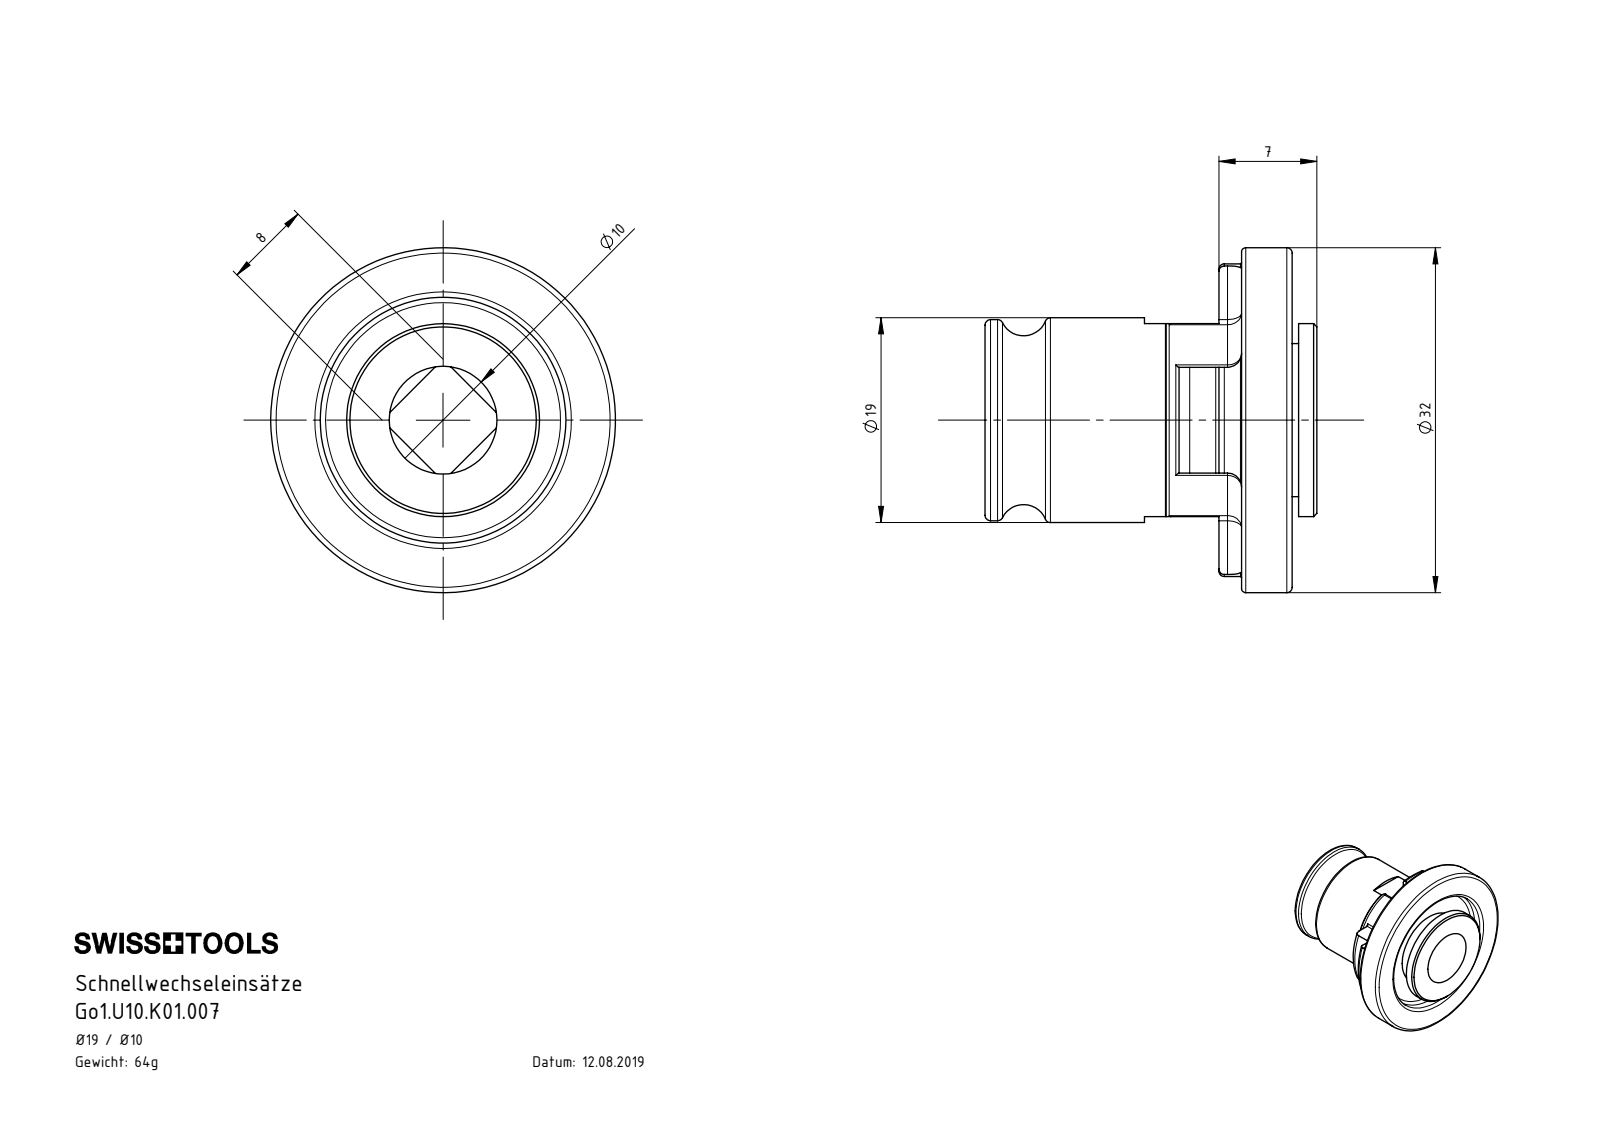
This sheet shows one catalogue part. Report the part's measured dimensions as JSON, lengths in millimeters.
{"part_name": "Go1.U10.K01.007", "step_written_by": "SolidWorks 2017 (AUTOMOTIVE_DESIGN)", "units": "millimeters", "bodies": {"solids": 1, "faces": 113, "planar": 36, "cylindrical": 32, "other": 45}, "overall_size": [32, 32, 30.8], "volume_mm3": 8171, "surface_area_mm2": 4952, "round_holes": [[10, 1], [11.4, 1], [22.8, 1]], "round_bosses_or_shafts": [[32, 1], [19, 1], [18.65, 1], [18.52, 1], [17.9, 1], [14.2, 1]], "partial_cylinders_radius": [[0.5, 8], [1.3, 4], [12.4, 1], [14.5, 1]], "face_to_face_distances": [2.35, 4.7, 7, 4.65, 2.3, 23.8, 26.15, 28.5, 30.8, 29.1]}
